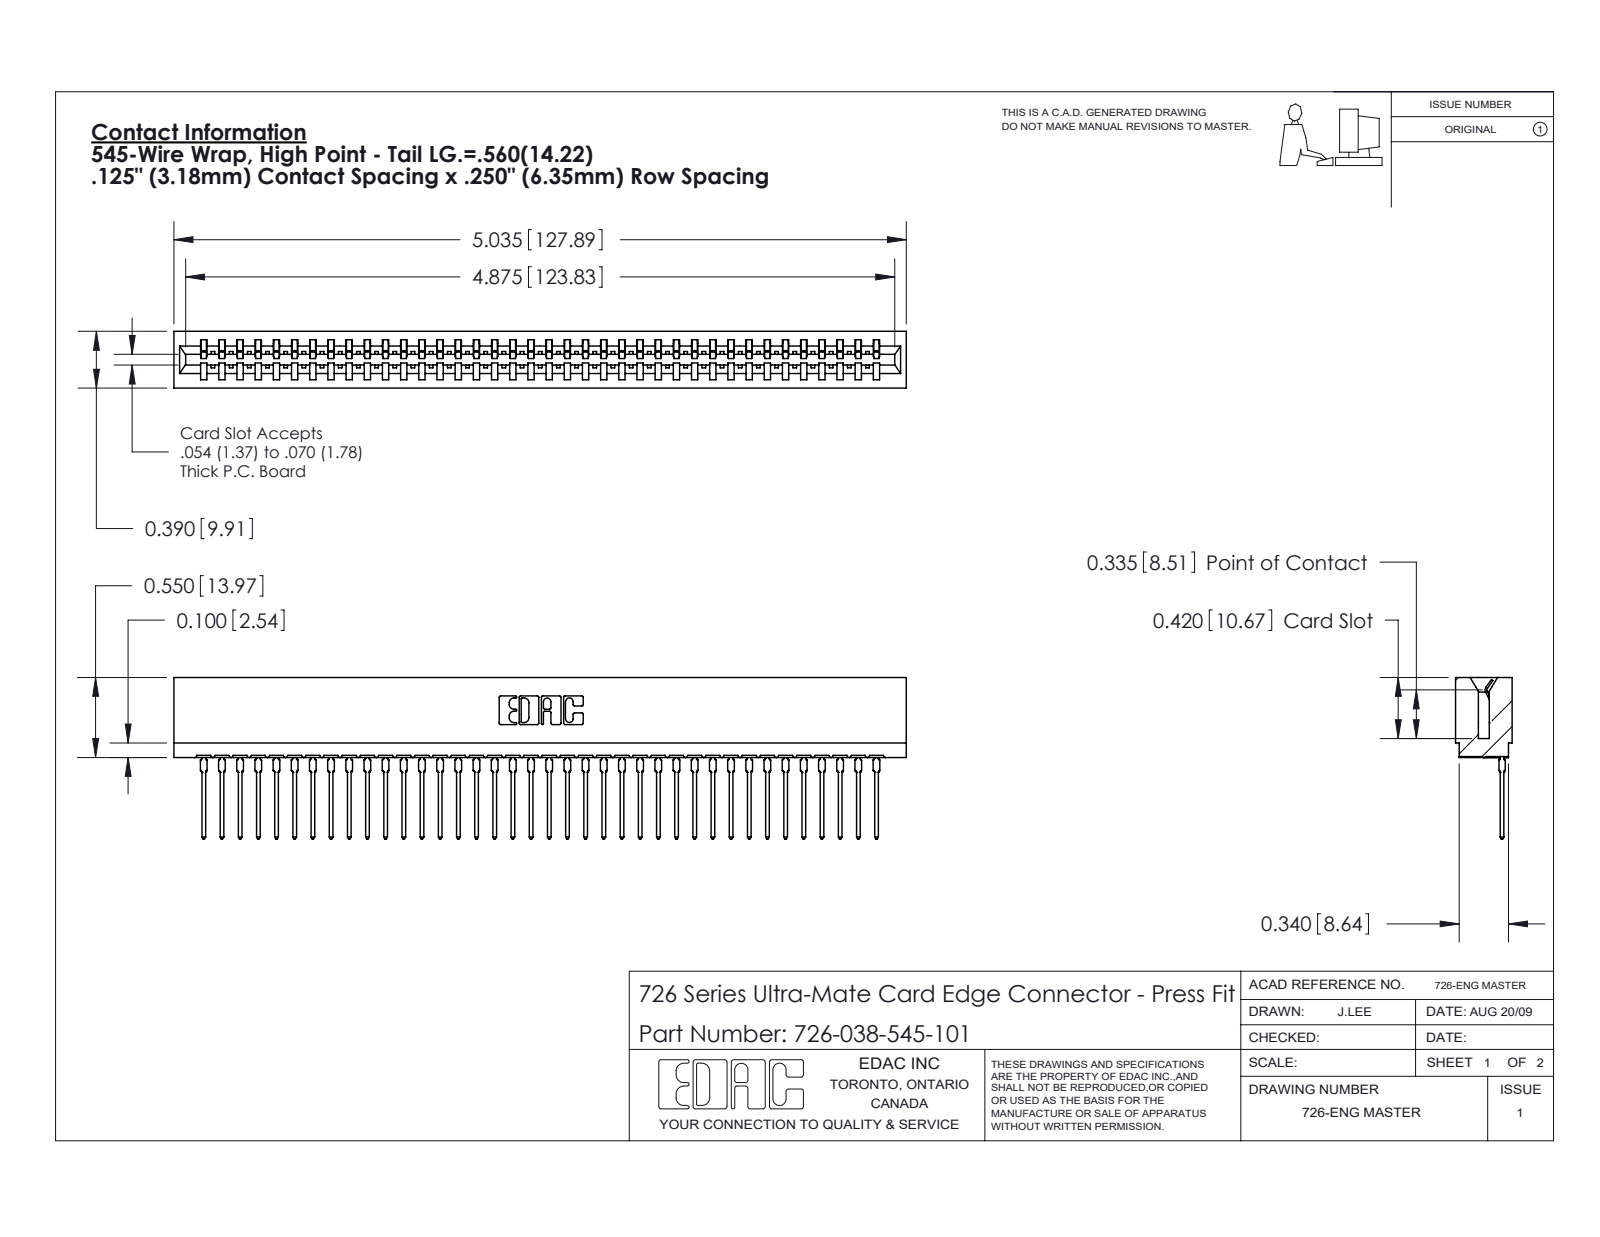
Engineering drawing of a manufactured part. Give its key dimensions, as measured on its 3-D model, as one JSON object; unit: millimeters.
{"part_name": "726 Part_.515 Slot Depth - 01; 726-038-545-101; 746-292-001_545", "step_written_by": "SolidWorks 2020 (CONFIG_CONTROL_DESIGN)", "units": "millimeters", "bodies": {"solids": 39, "faces": 4201, "planar": 2449, "cylindrical": 764, "other": 988}, "overall_size": [127.9, 28.2, 9.9], "volume_mm3": 11600, "surface_area_mm2": 18100, "partial_cylinders_radius": [[0.5, 76], [0.4, 39], [0.3, 22], [0.2, 6], [0.8, 6], [0.1, 4], [0.3, 4], [0.7, 3]], "face_to_face_distances": [1.4, 8.5, 9.9, 6.4, 0.6, 7.8, 2.1, 7, 12.7, 9.3]}
